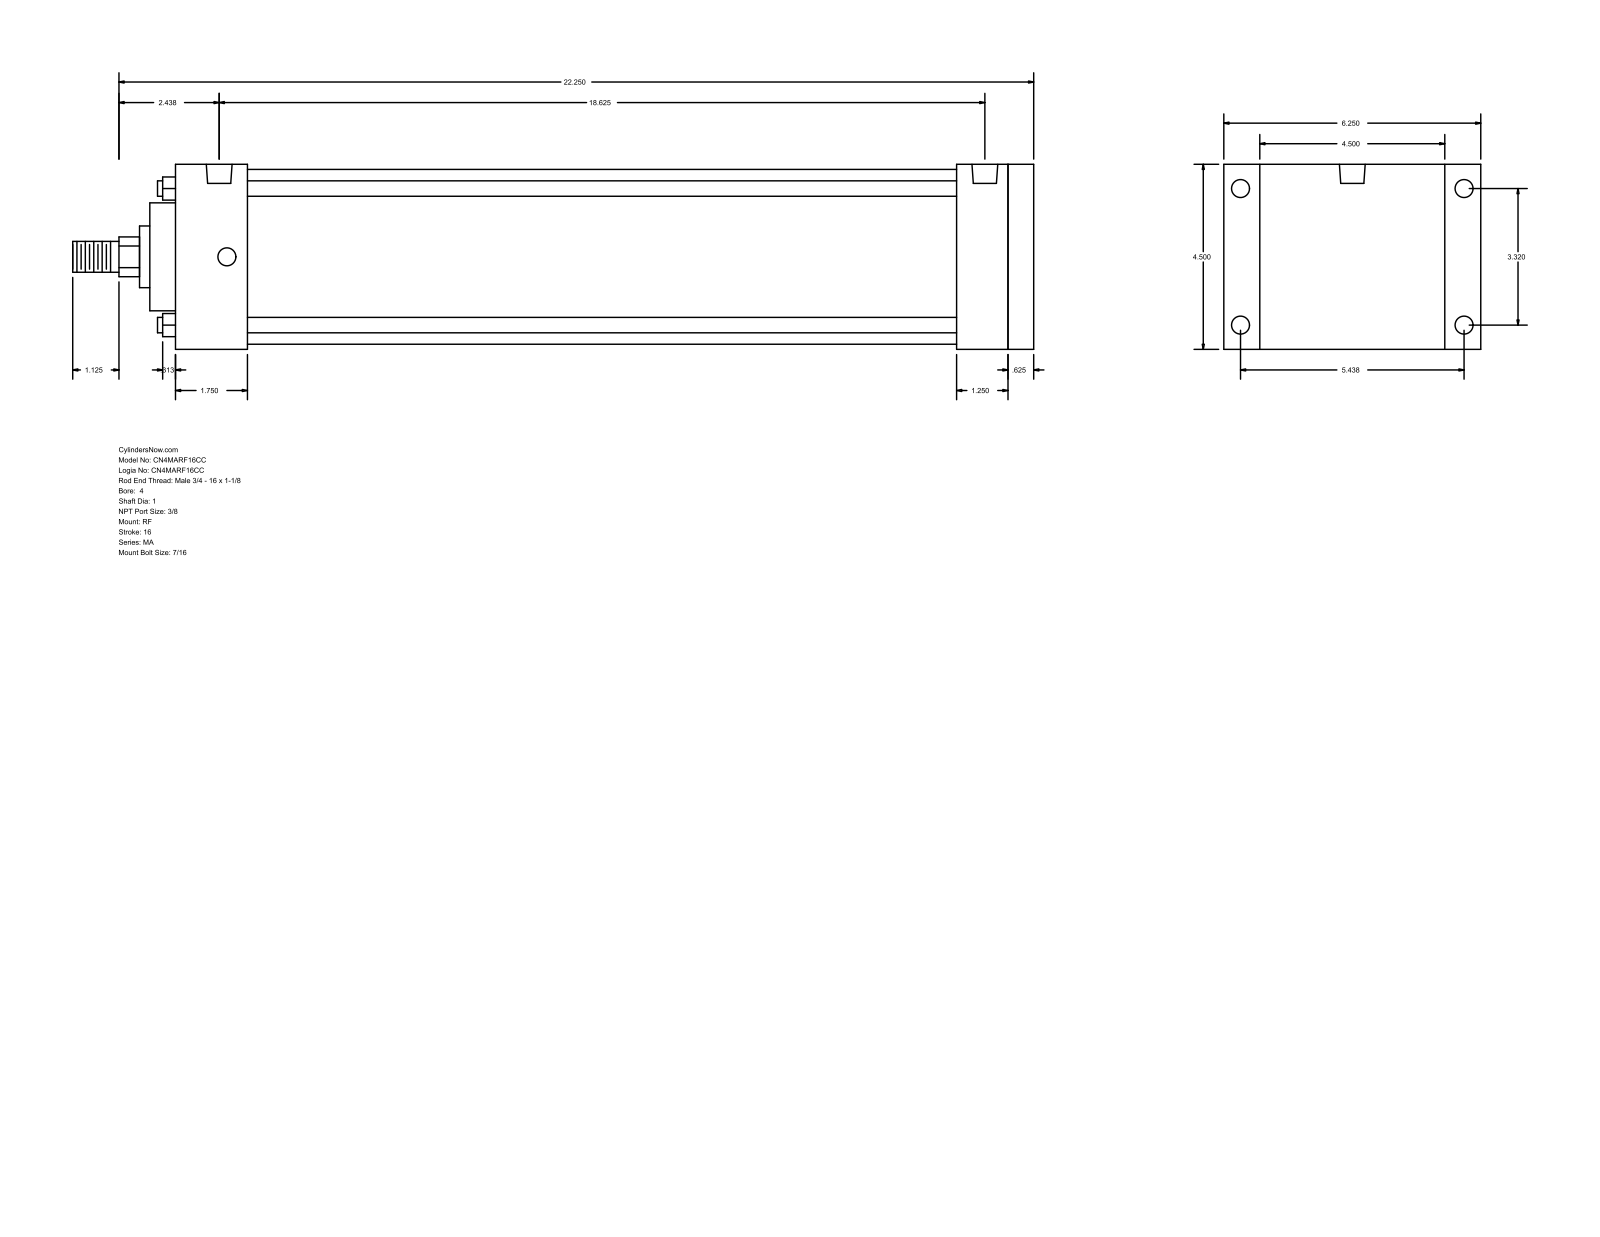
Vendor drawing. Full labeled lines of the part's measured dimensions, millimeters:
Part name (STEP PRODUCT): MA_RF__0400_1
STEP written by: GSSL Pune (CONFIG_CONTROL_DESIGN)
Units: millimetres
Bodies: 0 solids, 94 faces (65 planar, 29 cylindrical, 0 other)
Overall size (bounding box): 593.73 × 158.75 × 114.3
Round holes (diameter × count): ⌀11.11 ×8, ⌀15.93 ×2
Round bosses / shafts (diameter × count): ⌀9.53 ×4, ⌀107.95 ×1, ⌀66.67 ×1, ⌀38.1 ×1, ⌀25.4 ×1, ⌀19.05 ×1
Partial cylindrical surfaces — rounded edges, fillets, slot ends (radius × count): R12.29 ×1
Main face-to-face distances: 114.3, 530.23, 514.35, 15.88, 22.23, 136.53, 482.6, 31.75, 47.63, 44.46
Hole centre spacings: 4.76, 84.32, 138.12, 161.82, 463.56, 468.32, 473.08
